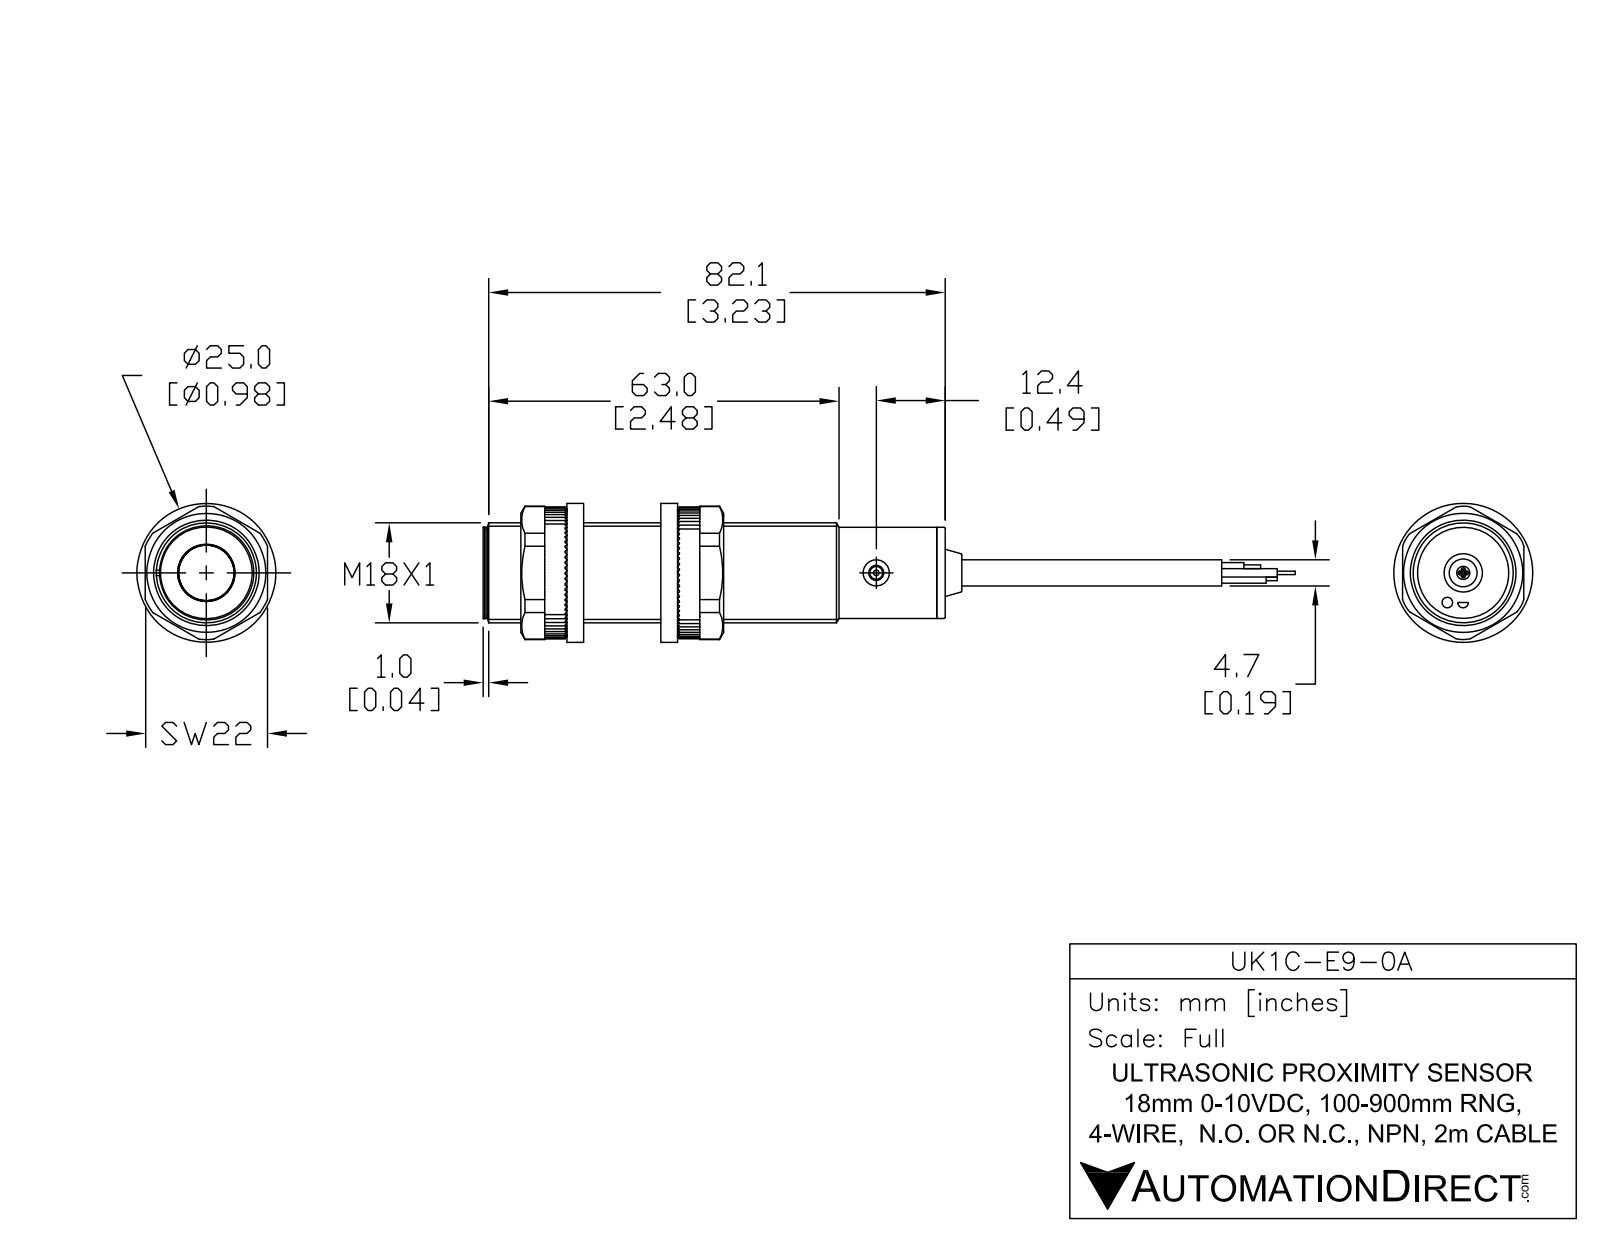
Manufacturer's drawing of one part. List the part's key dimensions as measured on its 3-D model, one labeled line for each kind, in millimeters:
Part name (STEP PRODUCT): UK1C-E9-0A
STEP written by: SolidWorks 2017 (AUTOMOTIVE_DESIGN)
Units: millimetres
Bodies: 6 solids, 55 faces (17 planar, 24 cylindrical, 14 other)
Overall size (bounding box): 122.7 × 18 × 18
Volume: 21 060 mm³ · Surface area: 6 897 mm²
Round holes (diameter × count): ⌀4.7 ×2, ⌀2.7 ×1
Round bosses / shafts (diameter × count): ⌀18 ×1, ⌀16.4 ×1, ⌀15.8 ×1, ⌀9.5 ×1, ⌀4.8 ×1, ⌀2.3 ×1
Main face-to-face distances: 81.1, 82.6, 1.5, 1, 82.1, 83.6, 1, 82.1, 83.6, 82.7
